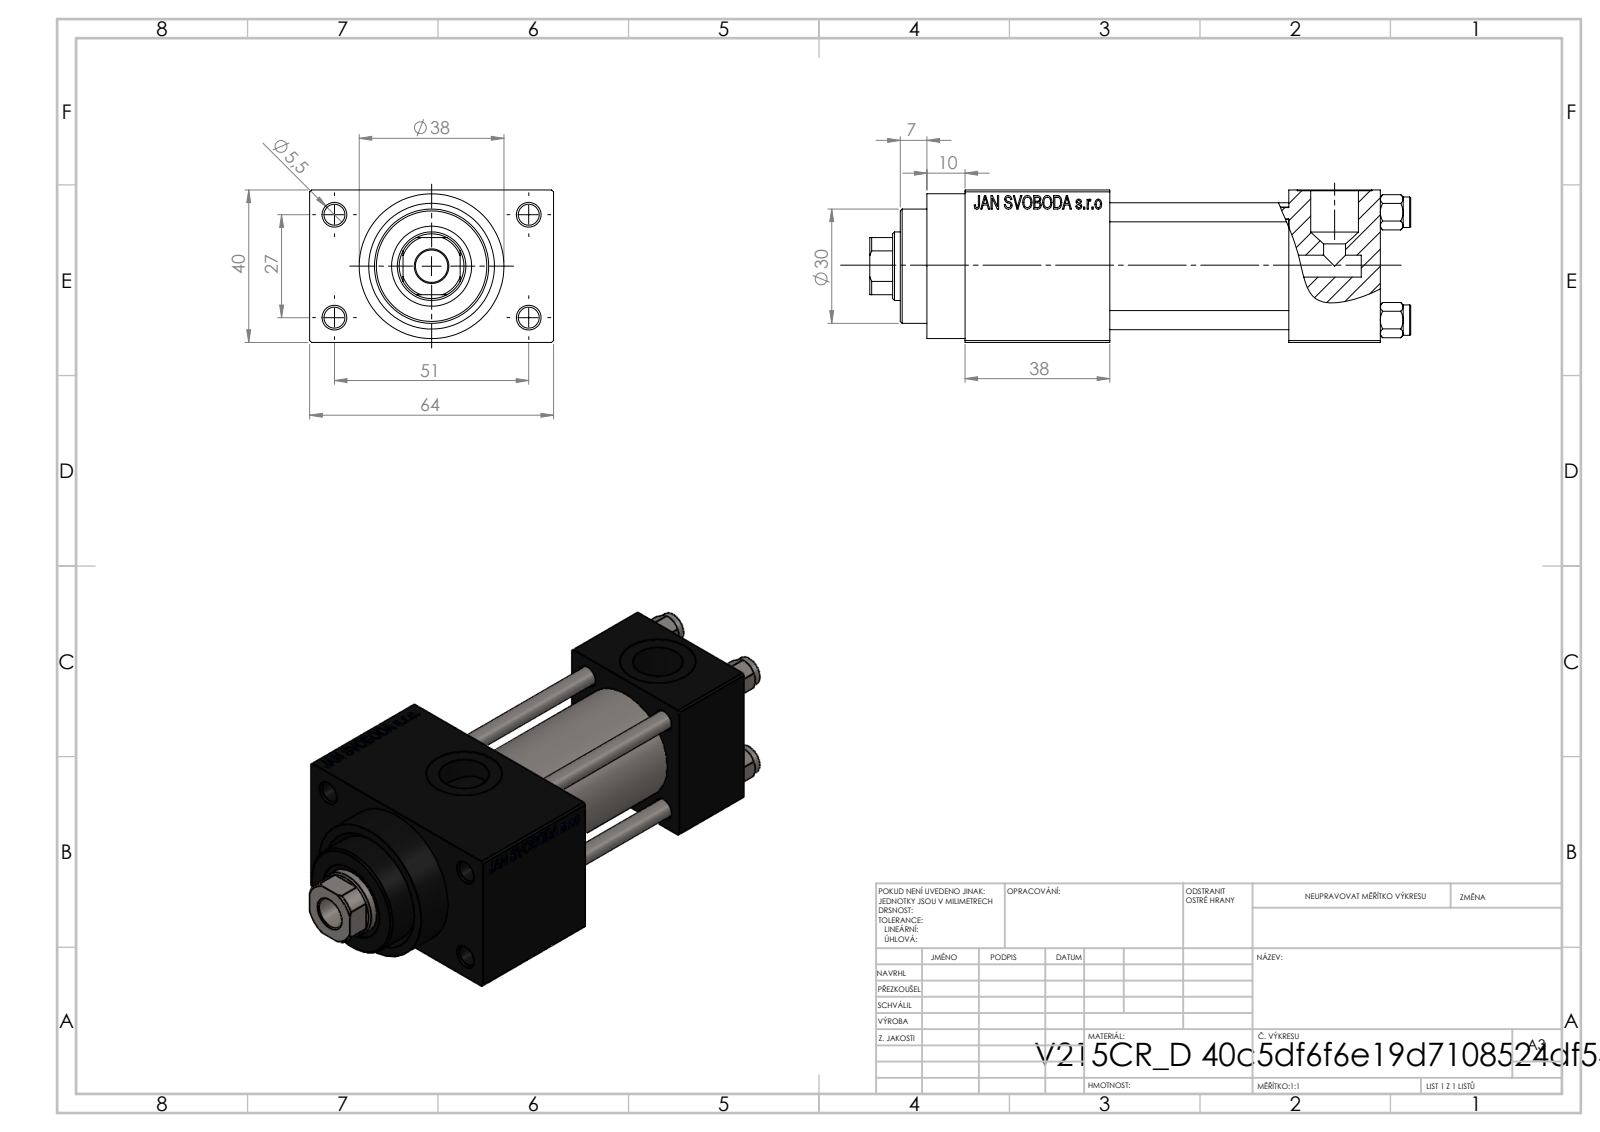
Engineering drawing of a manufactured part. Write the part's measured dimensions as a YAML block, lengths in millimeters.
part_name: "NUT_M5_D; V215_VC_A; V215CR_D_TYCINKA; V215CR_D_Body (+1 more)"
step_written_by: "SolidWorks 2019 (CONFIG_CONTROL_DESIGN)"
units: millimeters
bodies: {solids: 11, faces: 1102, planar: 495, cylindrical: 87, other: 520}
overall_size: [142, 64, 40]
volume: 180674
surface_area: 64134
round_holes:
  - {diameter: 5, count: 4}
  - {diameter: 5.5, count: 4}
  - {diameter: 20, count: 3}
  - {diameter: 7, count: 2}
  - {diameter: 13.16, count: 2}
  - {diameter: 8.5, count: 1}
  - {diameter: 18, count: 1}
  - {diameter: 21, count: 1}
  - {diameter: 25, count: 1}
  - {diameter: 30, count: 1}
round_bosses_or_shafts:
  - {diameter: 8, count: 4}
  - {diameter: 38, count: 1}
  - {diameter: 31, count: 1}
partial_cylinders:
  - {radius: 8.5, count: 1}
face_to_face_distances: [40, 12, 52, 47, 24, 71, 64, 38, 109, 85]
hole_center_spacings: [11.37, 20.01, 28.3, 28.85, 29.89, 39.66, 48.34, 27]
